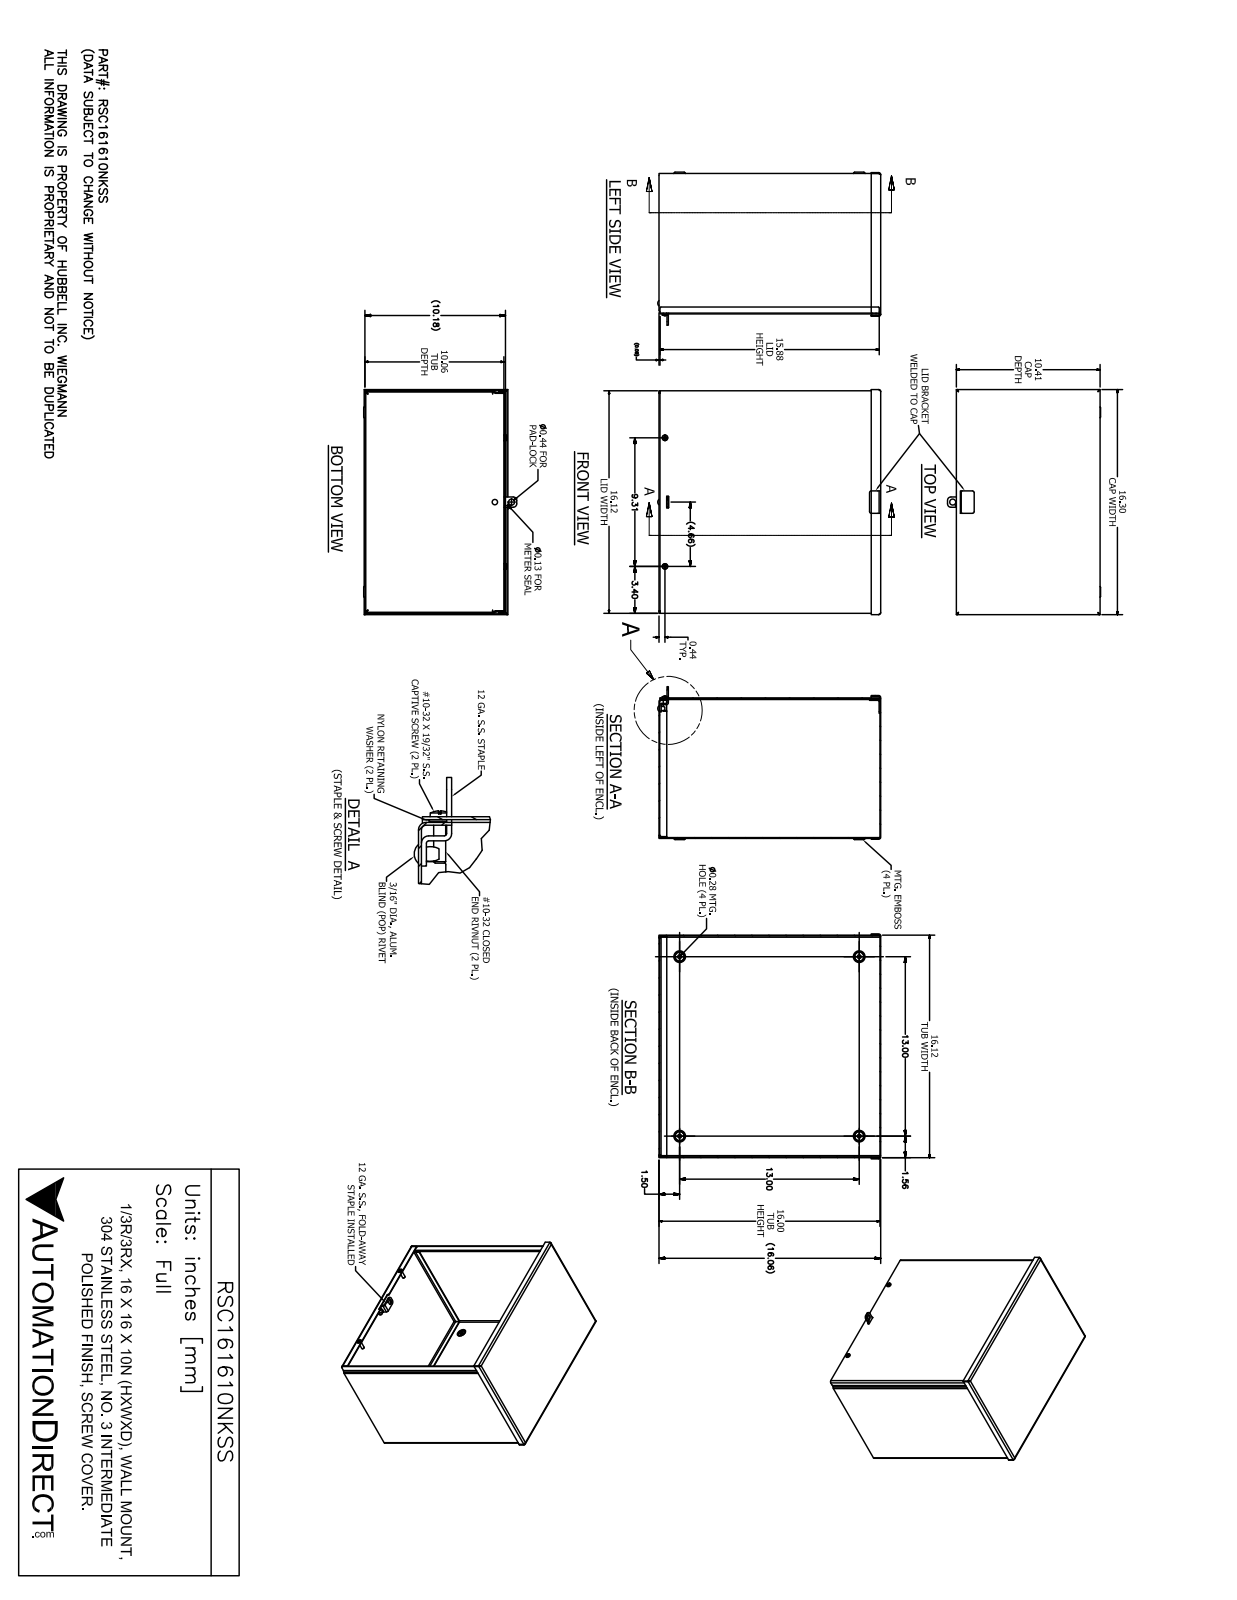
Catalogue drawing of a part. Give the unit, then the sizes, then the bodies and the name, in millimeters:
Units: millimetres
Overall size (bounding box): 414 × 410.2 × 281.5
Round holes (diameter × count): ⌀6.4 ×4, ⌀7.1 ×4, ⌀4 ×2, ⌀5 ×2, ⌀6.5 ×2, ⌀7.1 ×2, ⌀3.2 ×1, ⌀5 ×1, ⌀5.1 ×1, ⌀11.1 ×1
Round bosses / shafts (diameter × count): ⌀11.5 ×2, ⌀10.3 ×2, ⌀6.3 ×2, ⌀4.2 ×2, ⌀4.7 ×1
Partial cylindrical surfaces — rounded edges, fillets, slot ends (radius × count): R2.4 ×17, R3.9 ×17, R0.8 ×6, R3.2 ×4, R6.4 ×4, R1.6 ×3, R1.2 ×2, R1.3 ×2
Main face-to-face distances: 1.5, 257, 406.4, 407.9, 258.5, 255.5, 404.9, 409.4, 3, 1.5
Hole centre spacings: 330.2, 54.1, 54.5, 236.6, 284.7, 284.7, 360.2, 361
Volume: 1 195 000 mm³ · Surface area: 1 606 000 mm²
Bodies: 13 solids, 383 faces (199 planar, 99 cylindrical, 85 other)
Part name (STEP PRODUCT): RSC161610NKSS
STEP written by: SolidWorks 2017 (AUTOMOTIVE_DESIGN)
